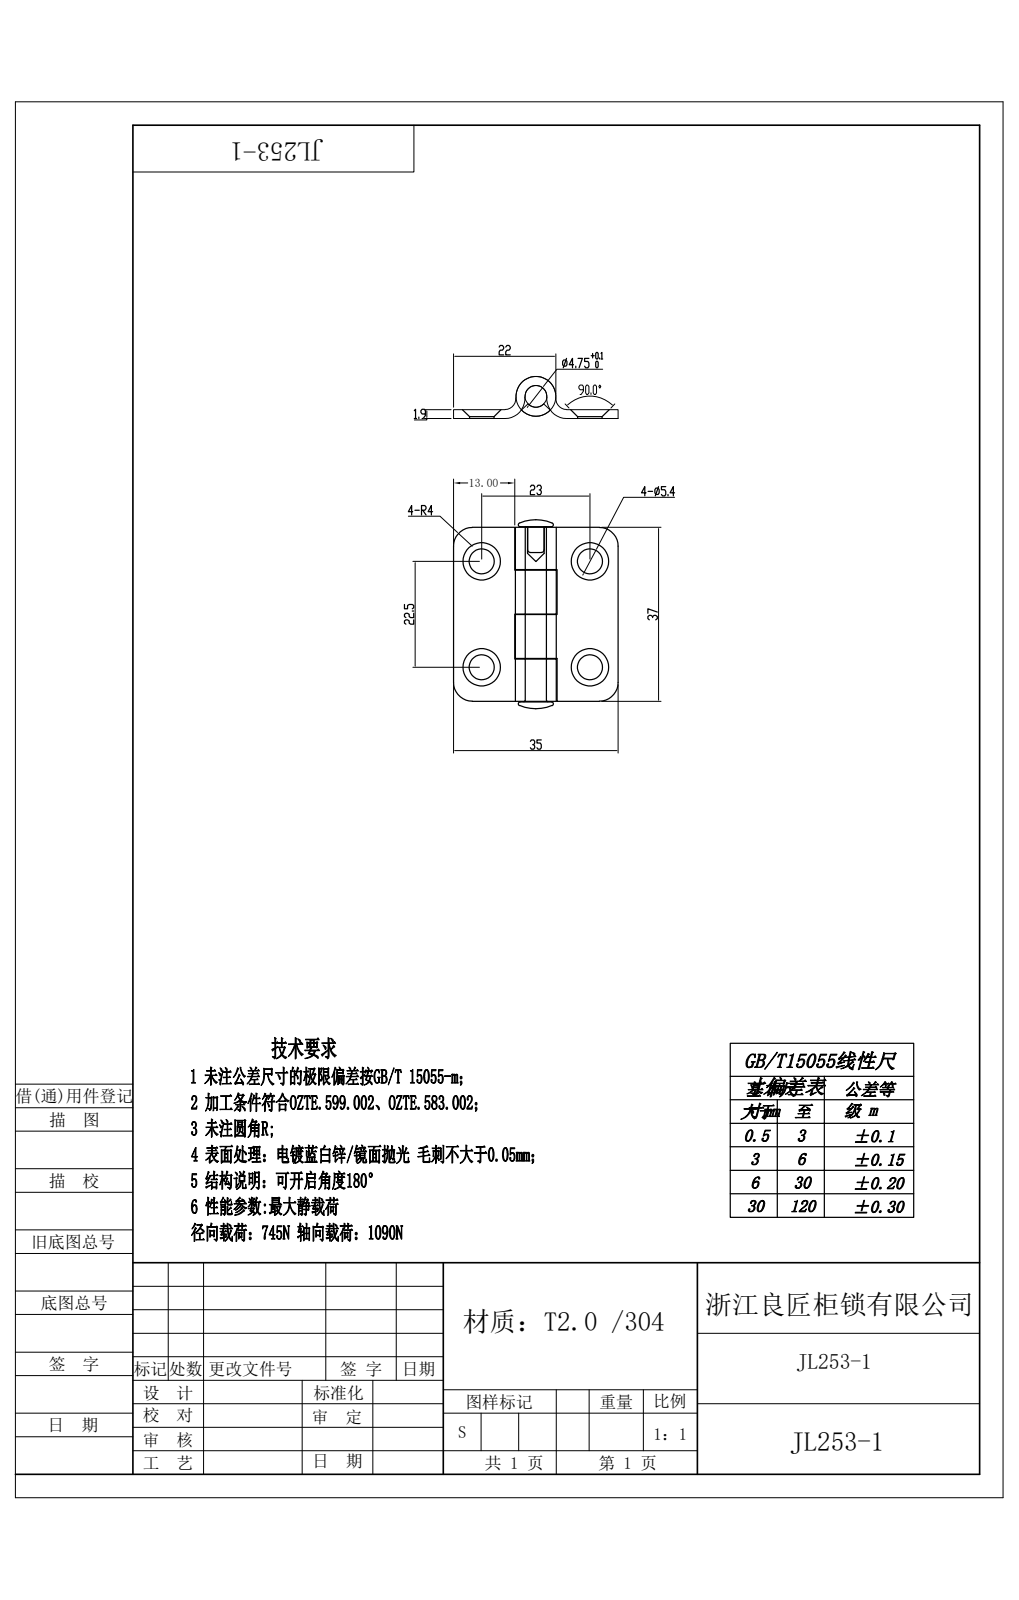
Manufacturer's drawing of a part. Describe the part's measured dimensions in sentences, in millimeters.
Its 3-D file was written by "Rhino 8.5 (CONFIG_CONTROL_DESIGN)". It is 4 solids with 80 faces: 24 planar, 32 cylindrical and 24 other. Overall it measures 40.29 by 35 by 9 millimeters. Its volume is 3 634 cubic millimeters and its surface area 4 835 square millimeters. Round holes: 4 of diameter 5.4, 1 of diameter 3.38, 1 of diameter 4.7. Round bosses or shafts: 1 of diameter 8.5, 1 of diameter 4.5. Partial cylindrical surfaces (rounded edges, fillets, slot ends): 4 of radius 4, 2 of radius 2.31, 2 of radius 4.25. The main face-to-face distances are 1.9, 9.5, 18.9, 9.4, 37, 11.23, 23.77, 35, 27.9, 9.1. The hole center spacings are 22.5, 23, 32.18.
